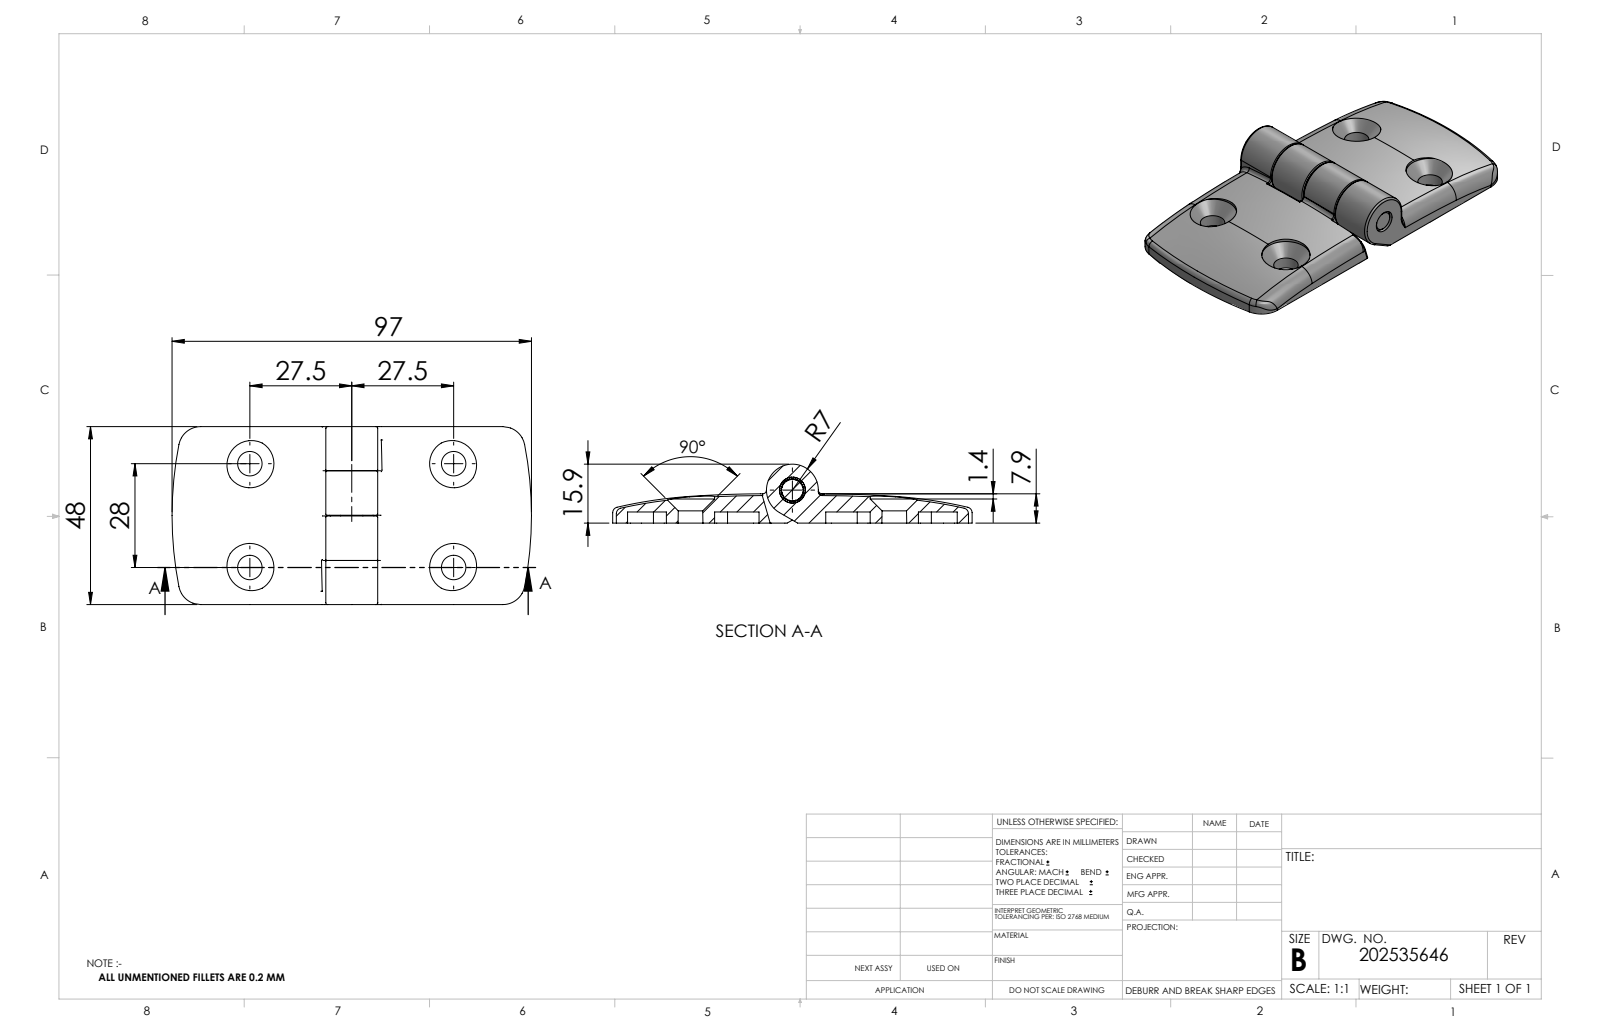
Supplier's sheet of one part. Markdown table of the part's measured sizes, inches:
| quantity | value |
| --- | --- |
| part name | 202535646_c_1 |
| STEP written by | SolidWorks 2014 (CONFIG_CONTROL_DESIGN) |
| units | inches |
| bodies | 7 solids, 500 faces (226 planar, 171 cylindrical, 103 other) |
| overall size | 3.819 × 1.89 × 0.63 |
| volume | 1.516 in³ |
| surface area | 27.7 in² |
| round holes (diameter × count) | 0.236 × 1 |
| round bosses / shafts (diameter × count) | 0.551 × 1, 0.276 × 1 |
| partial cylindrical surfaces (radius × count) | 0.059 × 20, 0.012 × 18, 0.197 × 8, 0.02 × 6, 0.118 × 4, 0.236 × 4, 0.256 × 4, 0.256 × 4 |
| main face-to-face distances | 0.118, 0.469, 1.421, 0.953, 1.89, 0.941, 0.949, 0.472, 0.48, 1.772 |
